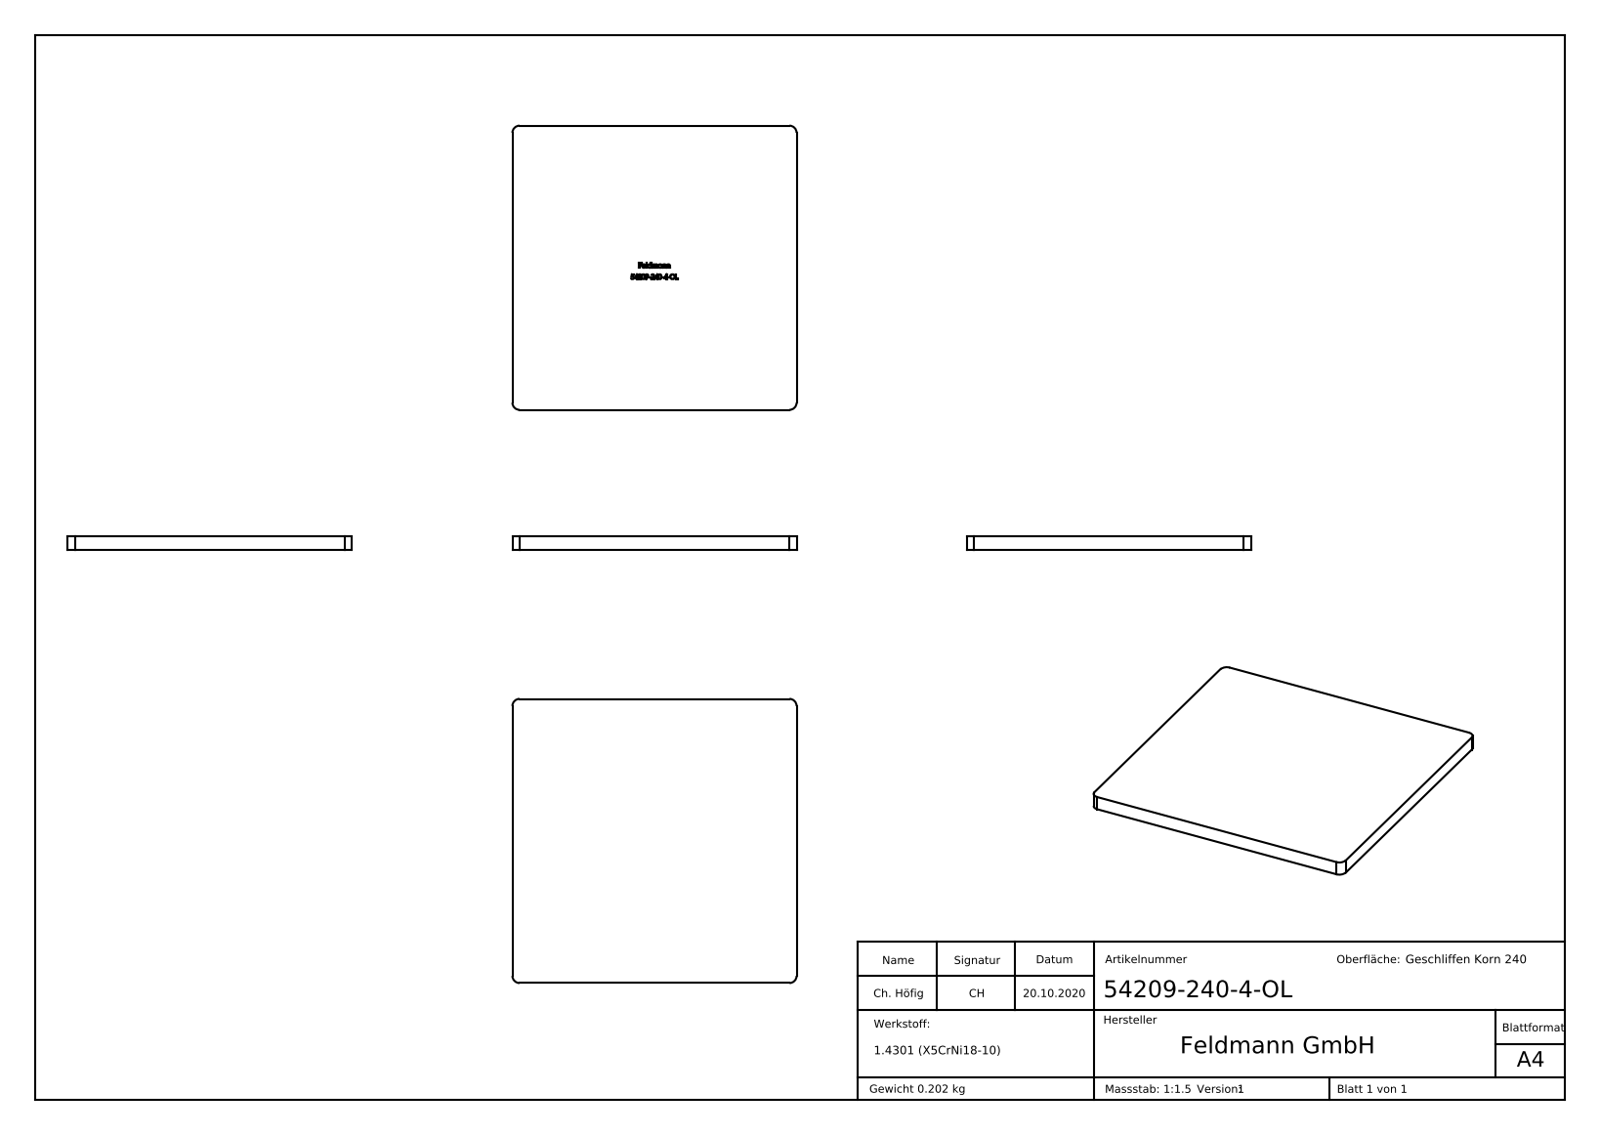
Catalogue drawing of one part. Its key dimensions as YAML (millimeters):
part_name: "54209-240-4-OL"
step_written_by: "SolidWorks 2018 (CONFIG_CONTROL_DESIGN)"
units: millimeters
bodies: {solids: 1, faces: 277, planar: 170, cylindrical: 4, other: 103}
overall_size: [80, 80, 4]
volume: 25586
surface_area: 14071
partial_cylinders:
  - {radius: 2, count: 4}
face_to_face_distances: [4, 80, 3.9, 0.44, 2.64, 5.7, 37.25, 42.75, 36.81, 43.19]
